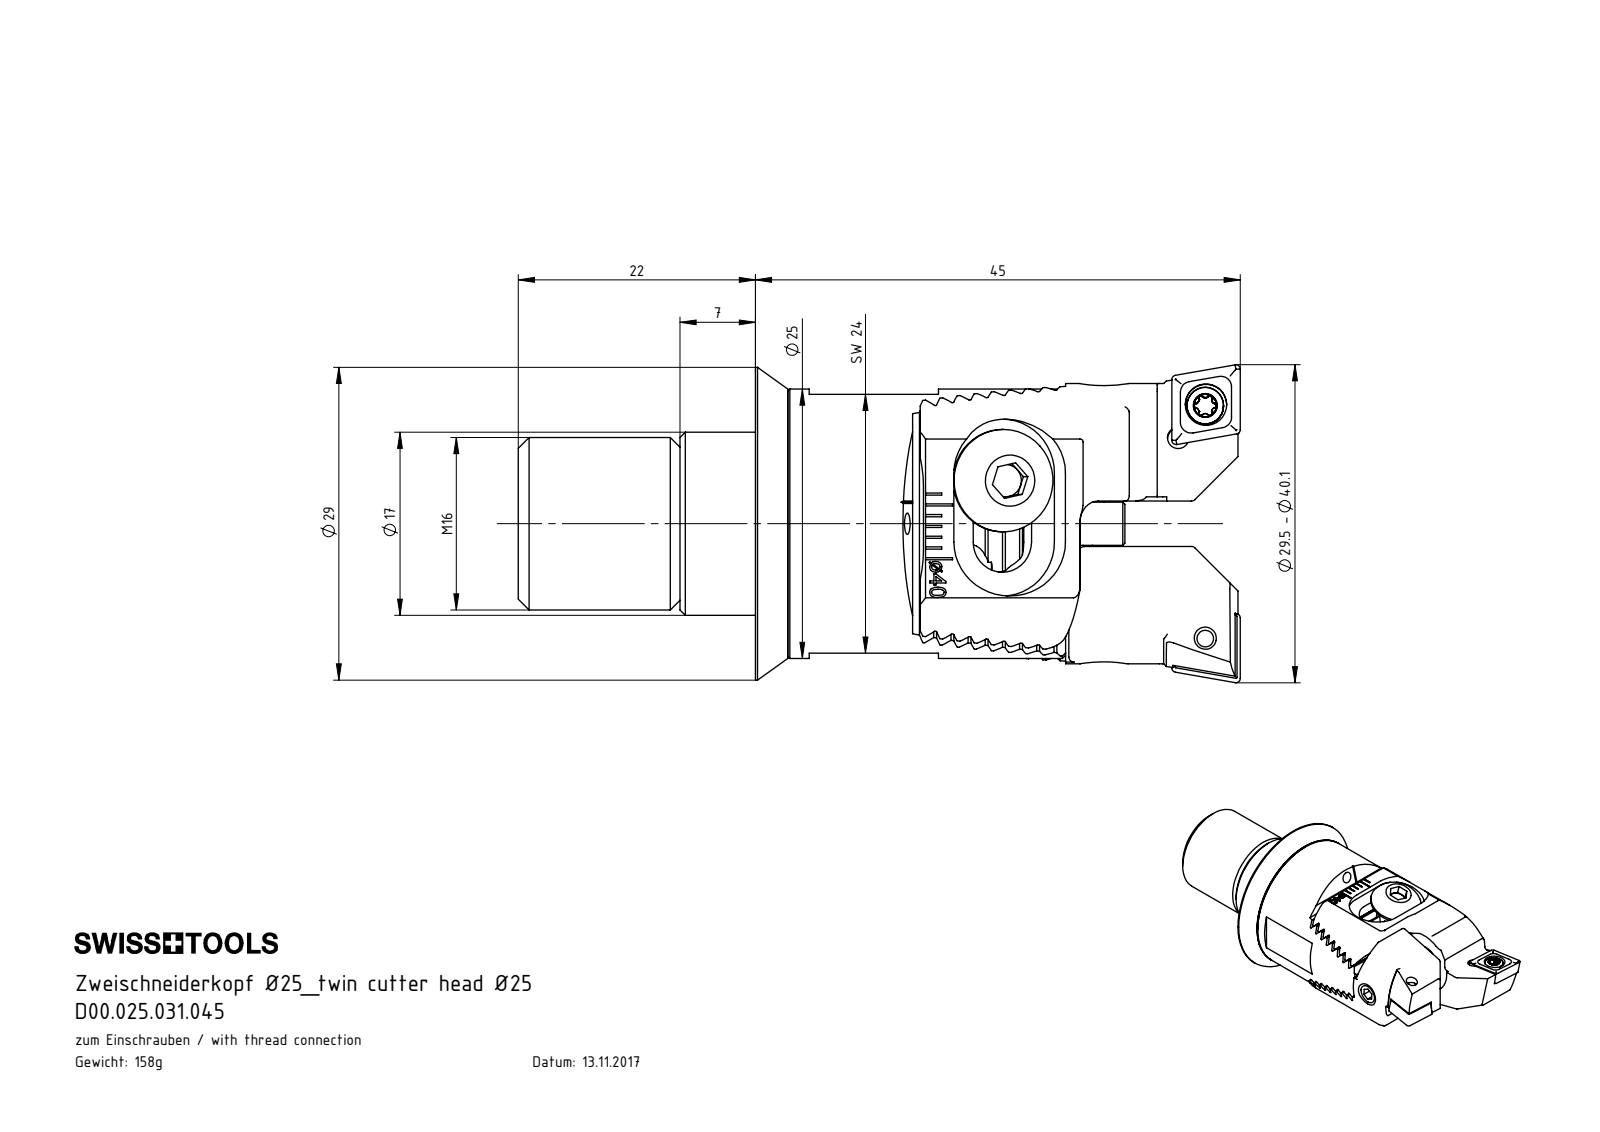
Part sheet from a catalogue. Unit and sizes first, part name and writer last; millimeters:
Units: millimetres
Overall size (bounding box): 67 × 29.5 × 29
Round holes (diameter × count): ⌀2 ×6, ⌀1.6 ×2, ⌀2.05 ×2, ⌀2.8 ×2, ⌀3.85 ×2, ⌀4.2 ×2, ⌀6 ×2, ⌀2.5 ×1, ⌀3.3 ×1, ⌀3.5 ×1, ⌀5.3 ×1, ⌀10.6 ×1
Round bosses / shafts (diameter × count): ⌀9.5 ×2, ⌀5 ×2, ⌀4 ×2, ⌀3.4 ×2, ⌀2.5 ×2, ⌀29 ×1, ⌀28 ×1, ⌀25 ×1
Partial cylindrical surfaces — rounded edges, fillets, slot ends (radius × count): R0.12 ×18, R0.5 ×18, R0.12 ×16, R0.21 ×12, R0.36 ×10, R2 ×4, R2.8 ×4, R5 ×4
Main face-to-face distances: 1.43, 3, 2.86, 7.14, 5.71, 1.39, 1.47, 8.57, 4.28, 10
Hole centre spacings: 3.91, 4.01, 7, 19.06, 19.15, 21.97, 13.52, 15.9
Volume: 20 663 mm³ · Surface area: 14 861 mm²
Bodies: 17 solids, 1044 faces (504 planar, 256 cylindrical, 284 other)
Part name (STEP PRODUCT): D00.025.031.045; HP5-Z25.030.045_A; ZC2-xxx.001.016_A; WCA-ER2.001.006_A (+8 more)
STEP written by: SolidWorks 2017 (CONFIG_CONTROL_DESIGN)
